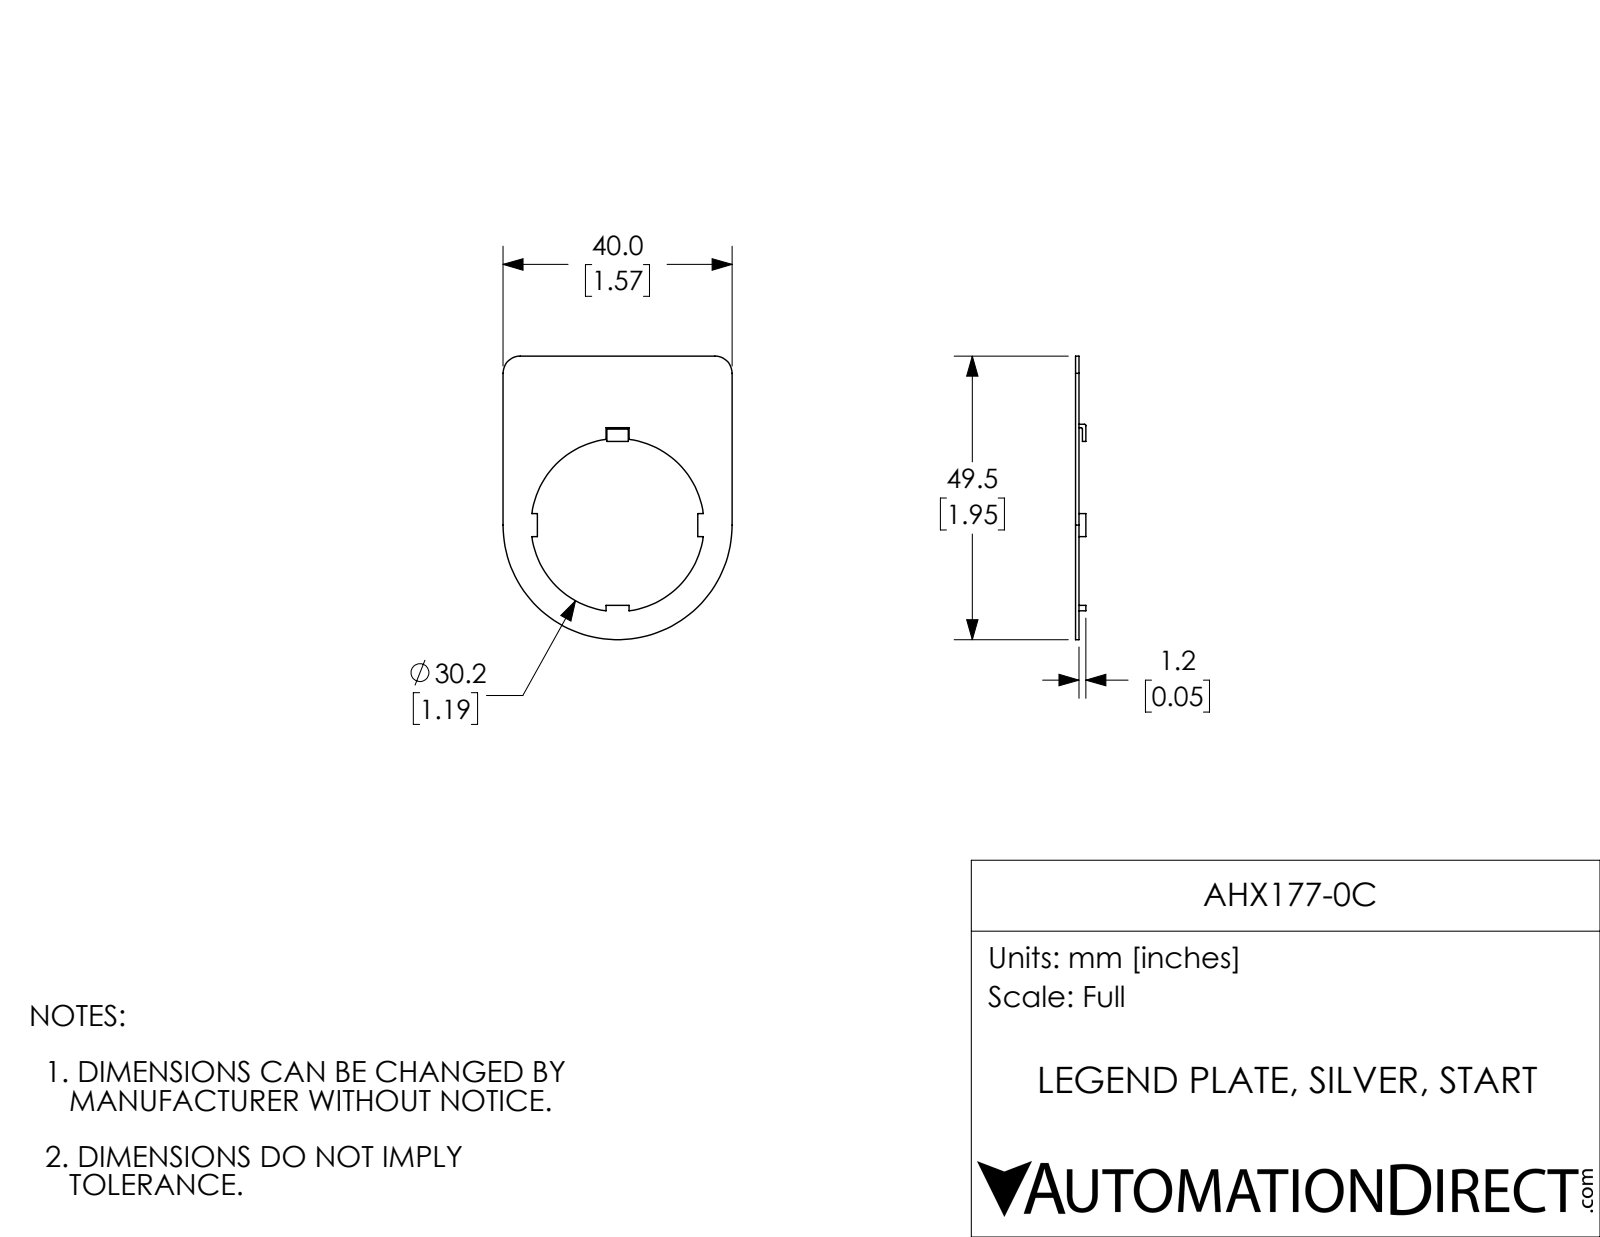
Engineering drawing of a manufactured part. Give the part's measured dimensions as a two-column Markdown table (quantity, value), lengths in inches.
| quantity | value |
| --- | --- |
| part name | AHX177-0C |
| STEP written by | SolidWorks 2017 (AUTOMOTIVE_DESIGN) |
| units | inches |
| bodies | 1 solid, 38 faces (29 planar, 9 cylindrical, 0 other) |
| overall size | 1.949 × 1.575 × 0.071 |
| volume | 0.041 in³ |
| surface area | 3.736 in² |
| round holes (diameter × count) | 1.189 × 1 |
| partial cylindrical surfaces (radius × count) | 0.01 × 2, 0.118 × 2, 0.787 × 1 |
| main face-to-face distances | 0.024, 0.047, 0.071, 1.575, 0.038, 0.236, 1.339, 0.198, 1.377, 1.141 |
